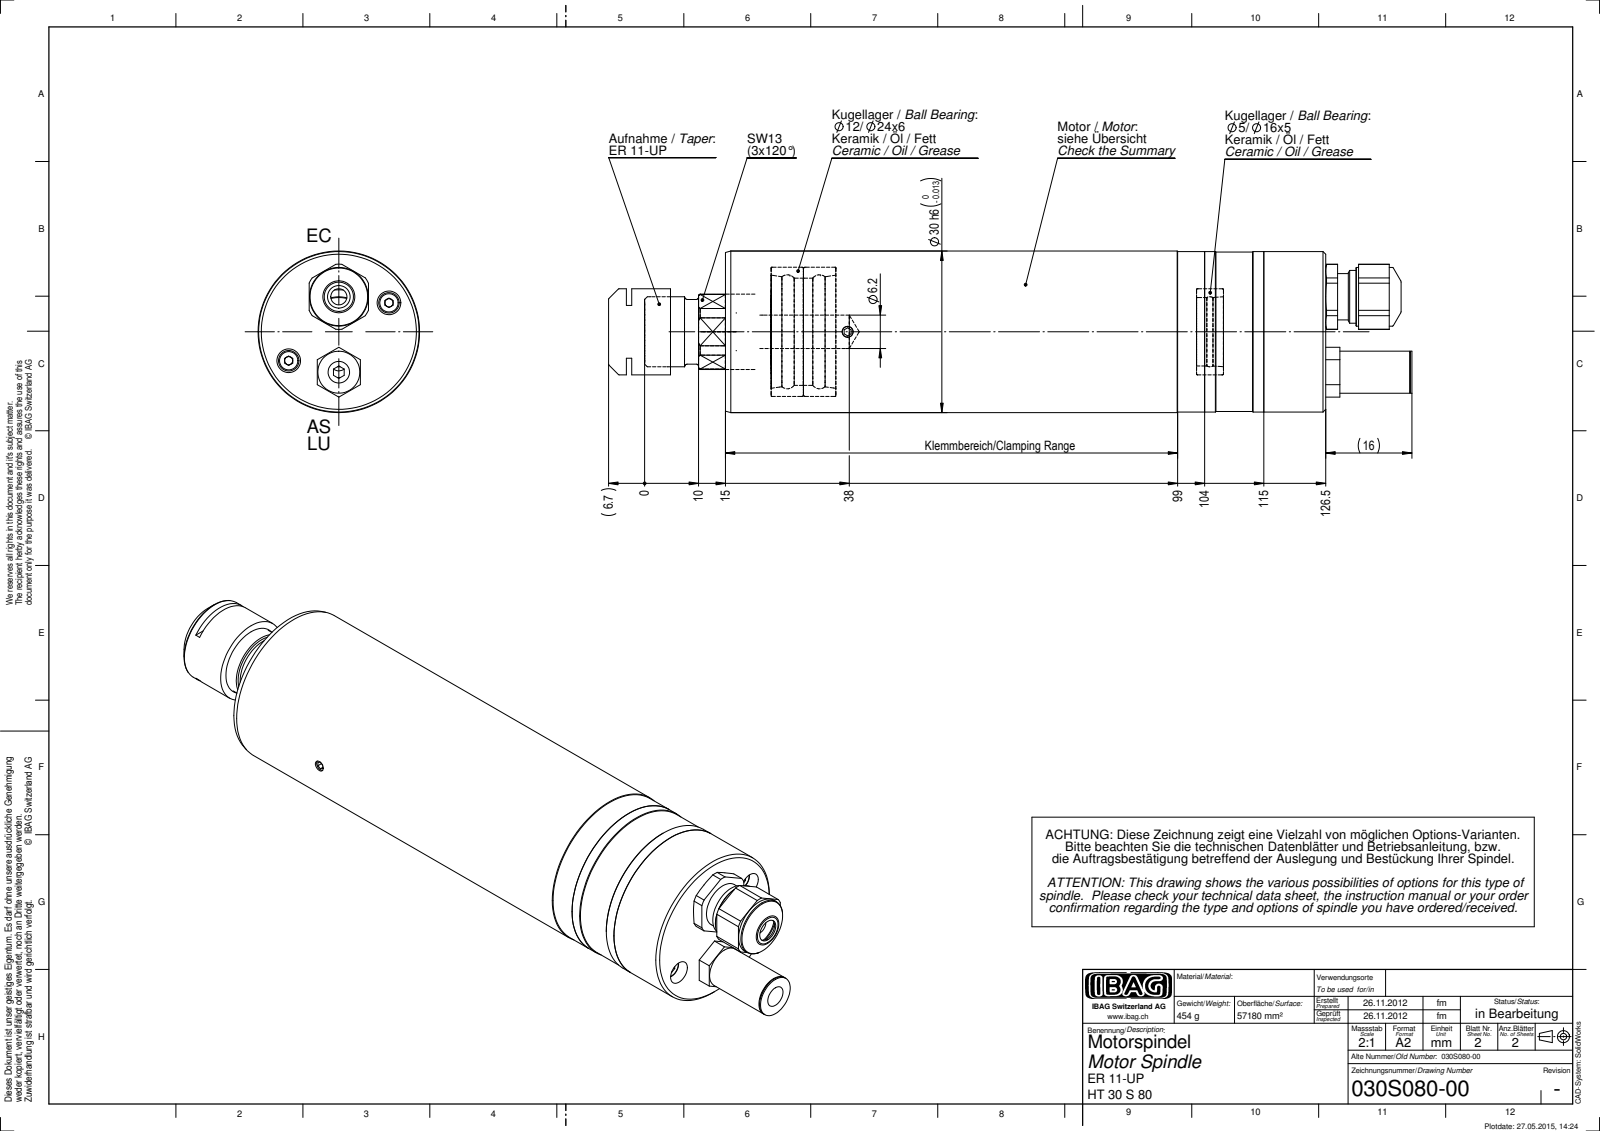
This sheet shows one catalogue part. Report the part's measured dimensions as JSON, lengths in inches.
{"part_name": "030S080-00", "step_written_by": "SolidWorks 2012 (CONFIG_CONTROL_DESIGN)", "units": "inches", "bodies": {"solids": 0, "faces": 262, "planar": 115, "cylindrical": 97, "other": 50}, "overall_size": [5.874, 1.181, 1.181], "round_holes": [[0.063, 4], [0.173, 2], [0.079, 1], [0.081, 1], [0.118, 1], [0.157, 1], [0.165, 1], [0.36, 1], [0.567, 1], [1.073, 1]], "round_bosses_or_shafts": [[1.181, 1], [1.173, 1], [1.165, 1], [0.63, 1], [0.551, 1], [0.512, 1], [0.472, 1], [0.429, 1]], "partial_cylinders_radius": [[0.059, 4], [0.063, 1], [0.238, 1]], "face_to_face_distances": [4.39, 3.504, 0.886, 0.25, 0.262, 0.433, 0.472, 0.039, 0.444, 0.432], "hole_center_spacings": [0.374, 0.529, 0.401, 0.423, 0.453, 0.476, 0.748, 0.77]}
